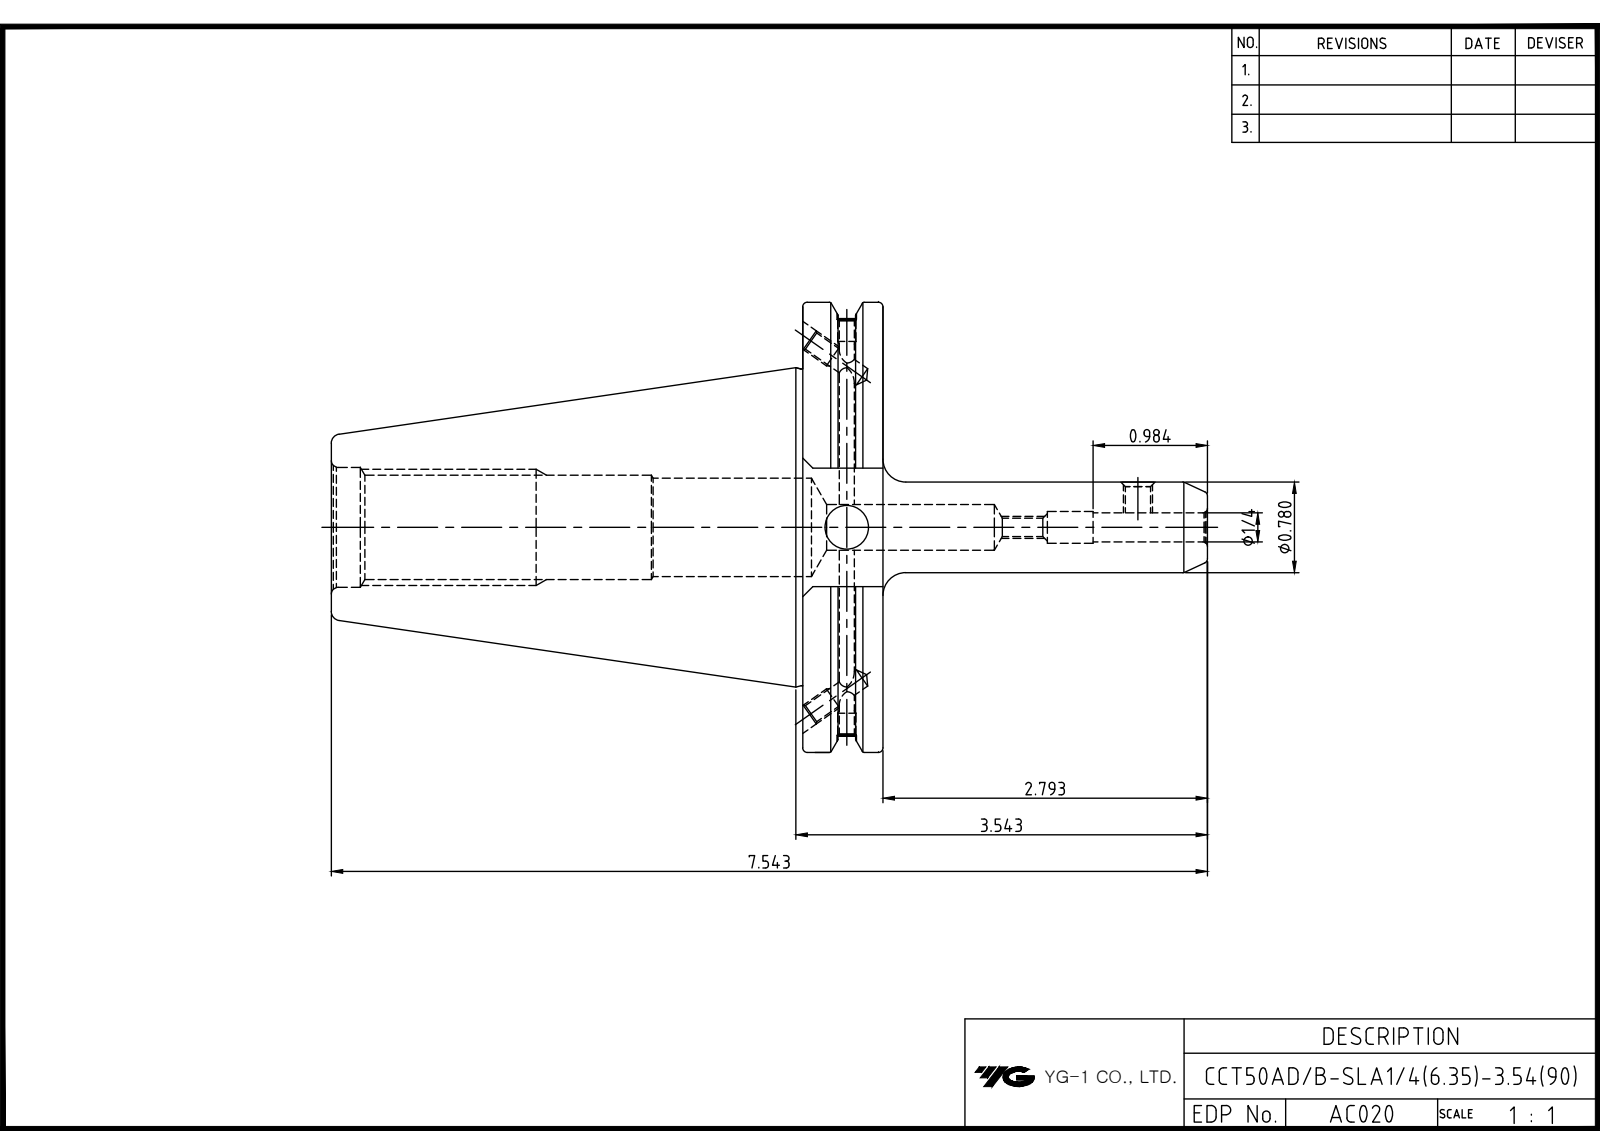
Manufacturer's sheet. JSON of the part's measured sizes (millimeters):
{"part_name": "LO-CCT50ADB-SLA6.35-90", "step_written_by": "Autodesk Inventor 2025 (AUTOMOTIVE_DESIGN)", "units": "millimeters", "bodies": {"solids": 1, "faces": 92, "planar": 39, "cylindrical": 28, "other": 25}, "overall_size": [191.6, 98.42, 94.69], "volume_mm3": 345557, "surface_area_mm2": 51071, "round_holes": [[3.24, 2], [4.13, 2], [4.2, 2], [5, 2], [3.96, 1], [5.36, 1], [6.35, 1], [7.55, 1], [9.53, 1], [10, 1], [21.97, 1], [26.2, 1]], "round_bosses_or_shafts": [[98.42, 1], [91.29, 1], [69.25, 1], [19.81, 1]], "face_to_face_distances": [17.55, 103.1, 120.65, 73.03, 25.9, 103.5, 0.4, 17.15, 114.64, 11.54]}
